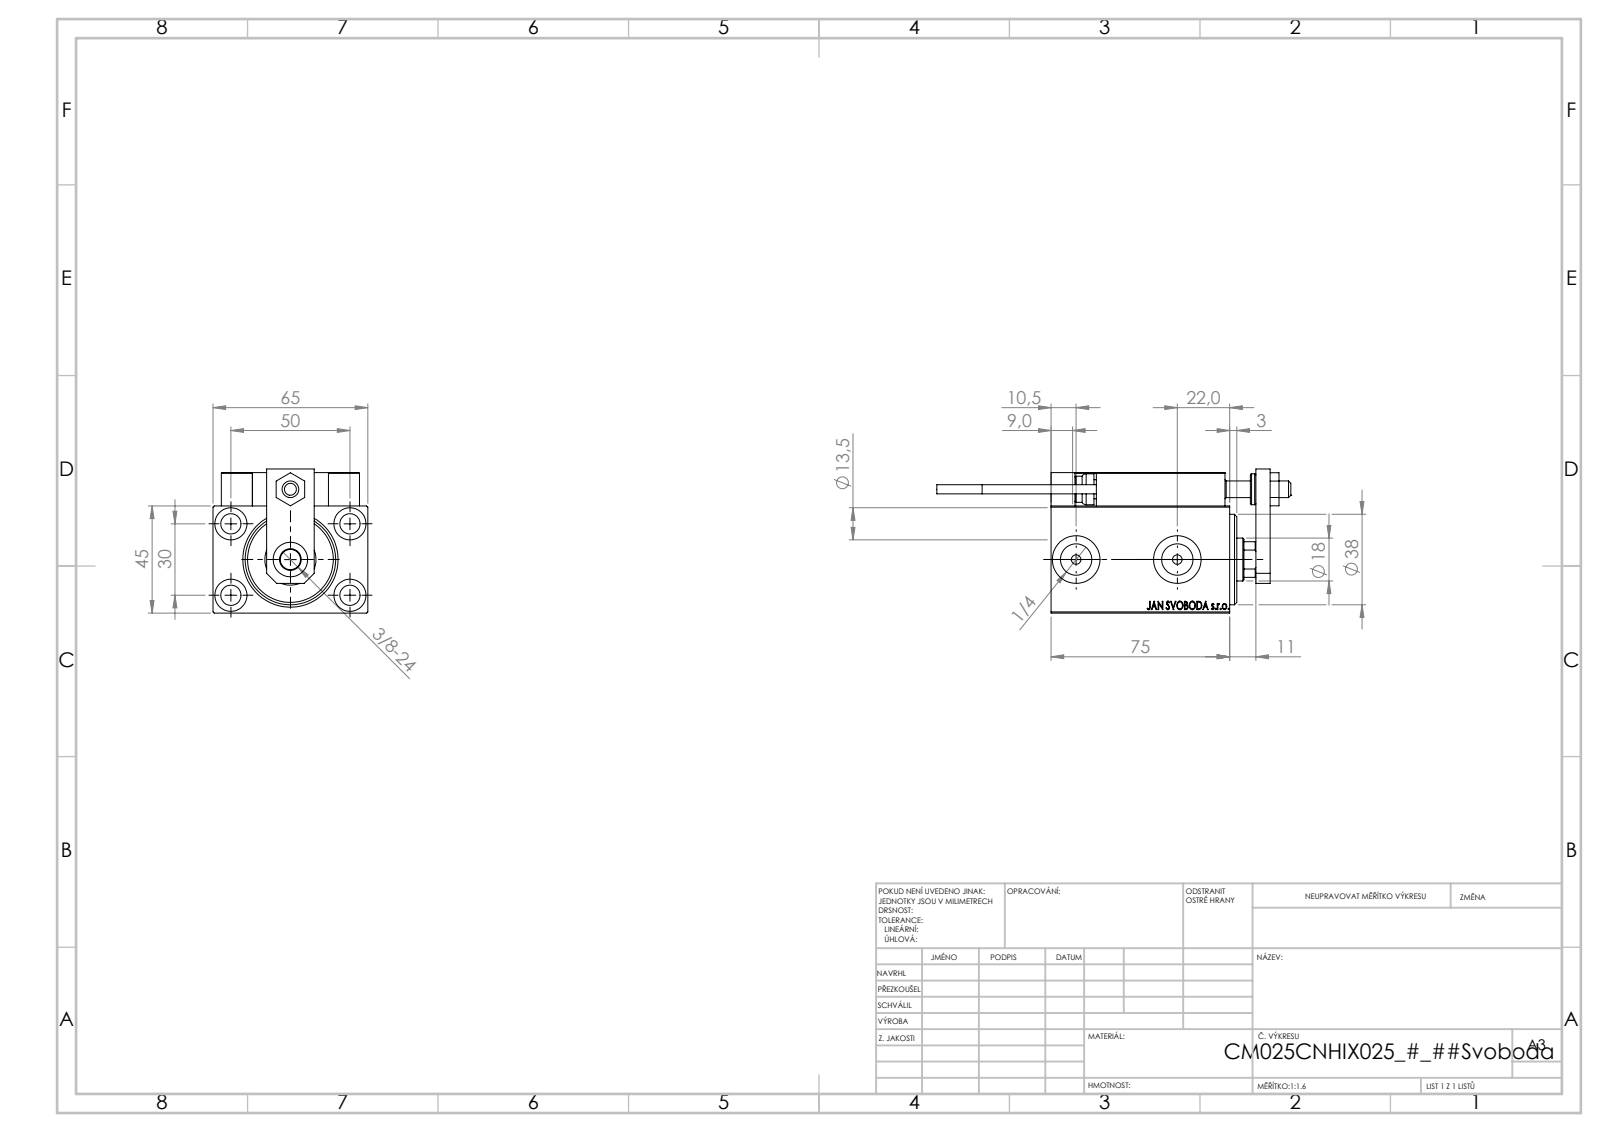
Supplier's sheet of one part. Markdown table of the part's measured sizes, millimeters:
| quantity | value |
| --- | --- |
| part name | V450CM_C_Body; TYC_L79; ZARAZKA; NUT_D12 (+7 more) |
| STEP written by | SolidWorks 2019 (CONFIG_CONTROL_DESIGN) |
| units | millimeters |
| bodies | 23 solids, 1282 faces (560 planar, 188 cylindrical, 534 other) |
| overall size | 148.7 × 65 × 60.5 |
| volume | 235 667 mm³ |
| surface area | 71 620 mm² |
| round holes (diameter × count) | 4 × 6, 8 × 5, 8.5 × 5, 3.2 × 4, 13.5 × 4, 5 × 2, 13.16 × 2, 20 × 2, 7 × 1, 14.5 × 1, 18 × 1, 21.5 × 1 |
| round bosses / shafts (diameter × count) | 5 × 2, 3.8 × 2, 13 × 1, 11 × 1 |
| partial cylindrical surfaces (radius × count) | 0.3 × 30, 3 × 2, 8.5 × 1 |
| main face-to-face distances | 45, 14, 65, 6, 59, 13, 3, 19, 3.5, 7 |
| hole center spacings | 29.15, 11.37, 20, 27.07, 28.9, 29.59, 29.69, 30 |
